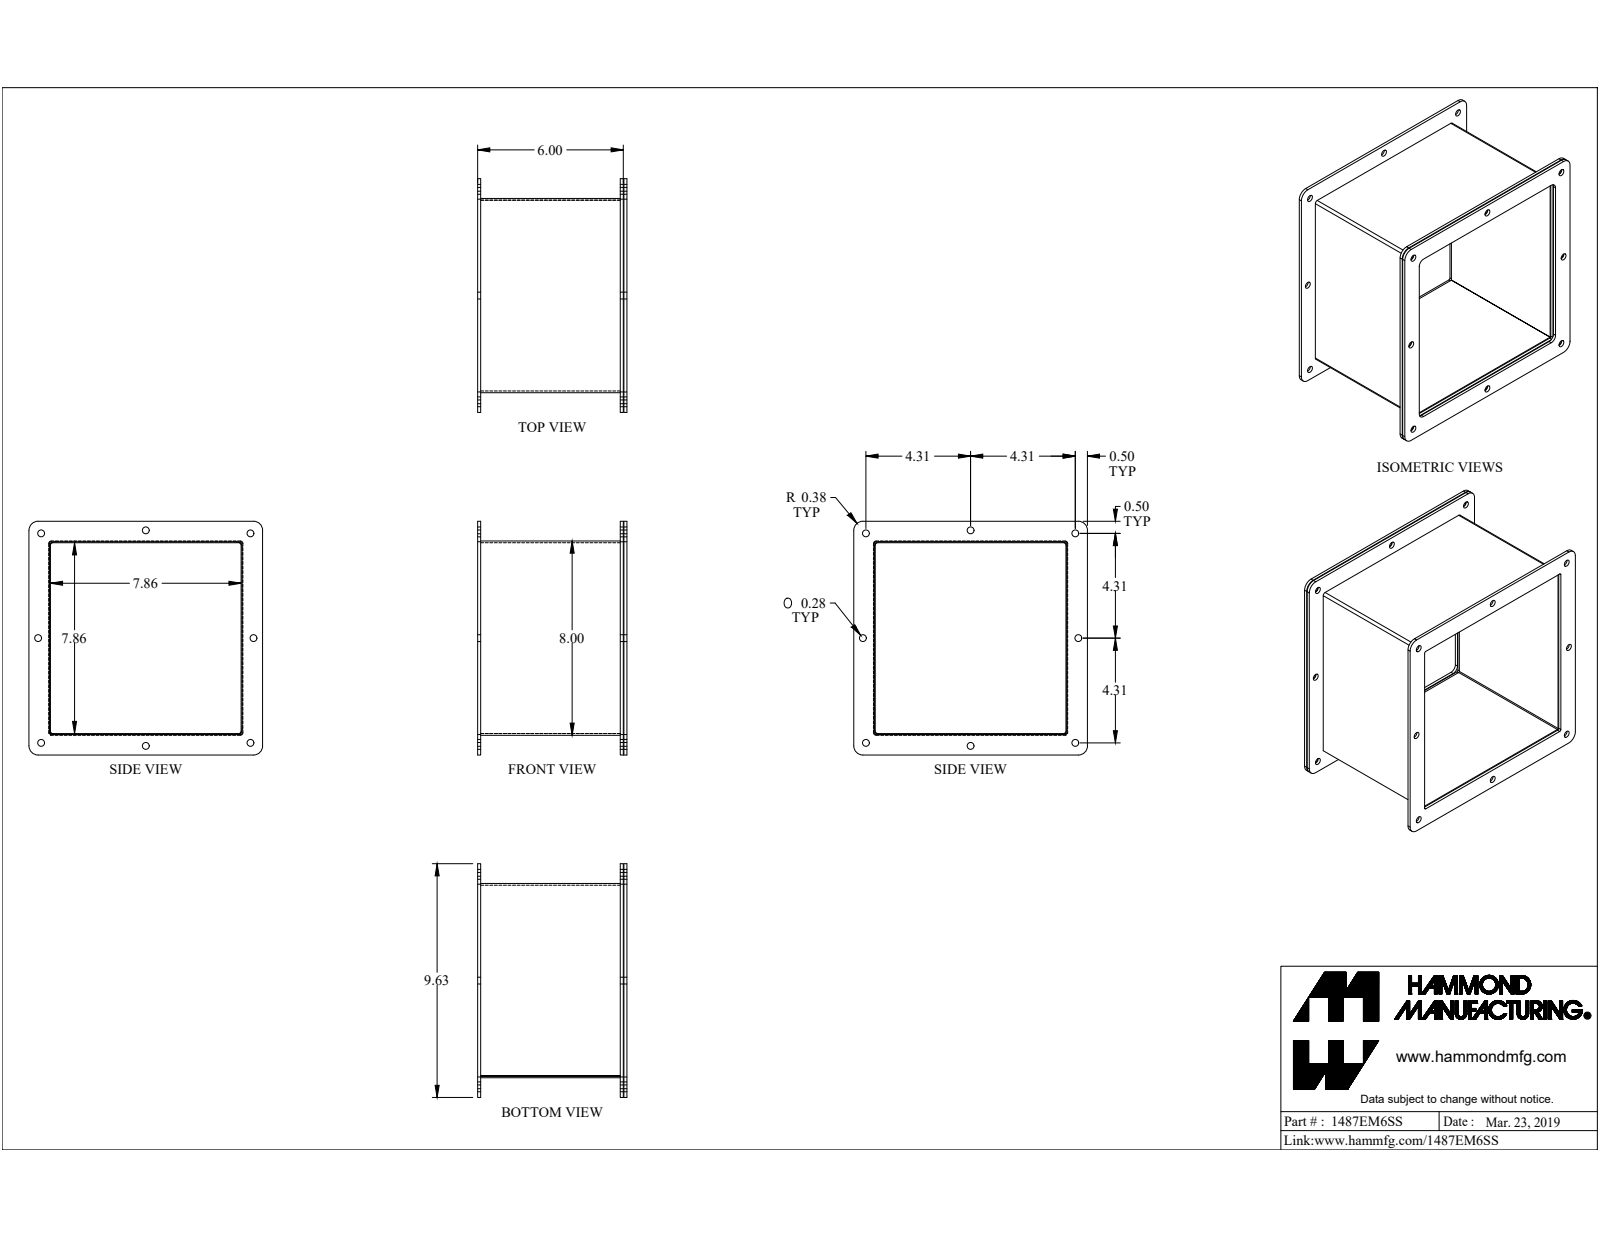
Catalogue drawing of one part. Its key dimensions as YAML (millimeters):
part_name: "1487EM6SS"
step_written_by: "SolidWorks 2019 (CONFIG_CONTROL_DESIGN)"
units: millimeters
bodies: {solids: 7, faces: 183, planar: 99, cylindrical: 76, other: 8}
overall_size: [244.5, 244.5, 166.9]
volume: 393900
surface_area: 369900
round_holes:
  - {diameter: 7.1, count: 8}
  - {diameter: 5, count: 1}
  - {diameter: 6.6, count: 1}
  - {diameter: 8.9, count: 1}
round_bosses_or_shafts:
  - {diameter: 12.7, count: 1}
  - {diameter: 6.4, count: 1}
partial_cylinders:
  - {radius: 0.5, count: 6}
  - {radius: 1.6, count: 4}
  - {radius: 6.4, count: 4}
  - {radius: 9.5, count: 4}
  - {radius: 0.9, count: 3}
  - {radius: 2.7, count: 3}
face_to_face_distances: [1.8, 201.4, 203.2, 199.5, 3.2, 149.2, 146.1, 3.8, 3.2, 153]
hole_center_spacings: [109.6, 247.8, 159.4, 219.1, 225.4, 309.8]
